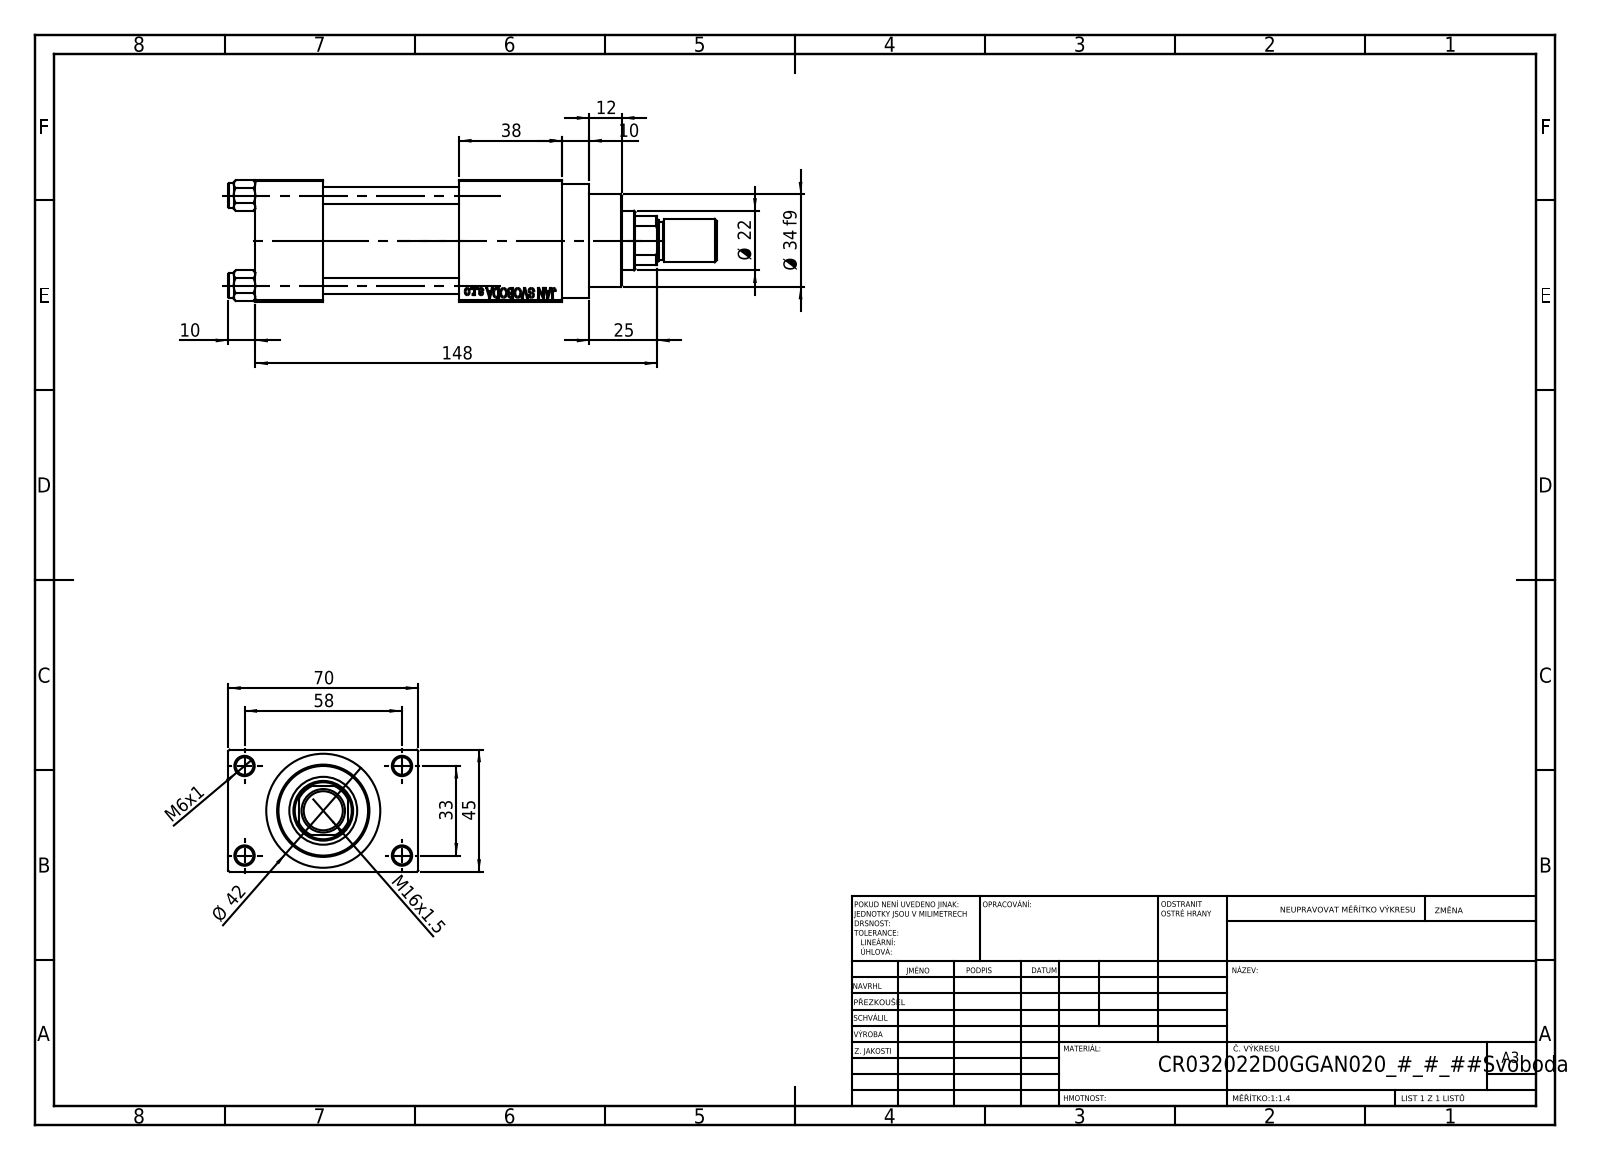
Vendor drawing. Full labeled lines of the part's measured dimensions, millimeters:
Part name (STEP PRODUCT): ROD_END_AH; NUT_M5_D; V215CR_D_TYCINKA; V215_VC_A (+2 more)
STEP written by: SolidWorks 2019 (CONFIG_CONTROL_DESIGN)
Units: millimetres
Bodies: 12 solids, 1117 faces (500 planar, 93 cylindrical, 524 other)
Overall size (bounding box): 180 × 70 × 45
Volume: 248 926 mm³ · Surface area: 80 997 mm²
Round holes (diameter × count): ⌀6 ×4, ⌀6.5 ×4, ⌀7 ×2, ⌀13.16 ×2, ⌀20 ×2, ⌀10.5 ×1, ⌀22 ×1, ⌀24 ×1, ⌀25 ×1, ⌀32 ×1, ⌀33 ×1
Round bosses / shafts (diameter × count): ⌀9 ×4, ⌀42 ×1, ⌀38 ×1, ⌀34 ×1, ⌀16 ×1, ⌀14 ×1
Partial cylindrical surfaces — rounded edges, fillets, slot ends (radius × count): R10.5 ×1
Main face-to-face distances: 45, 25, 12.5, 57.5, 50, 75, 88, 70, 38, 113
Hole centre spacings: 12.4, 23.48, 33.2, 33.37, 35.35, 45.6, 56.35, 33
